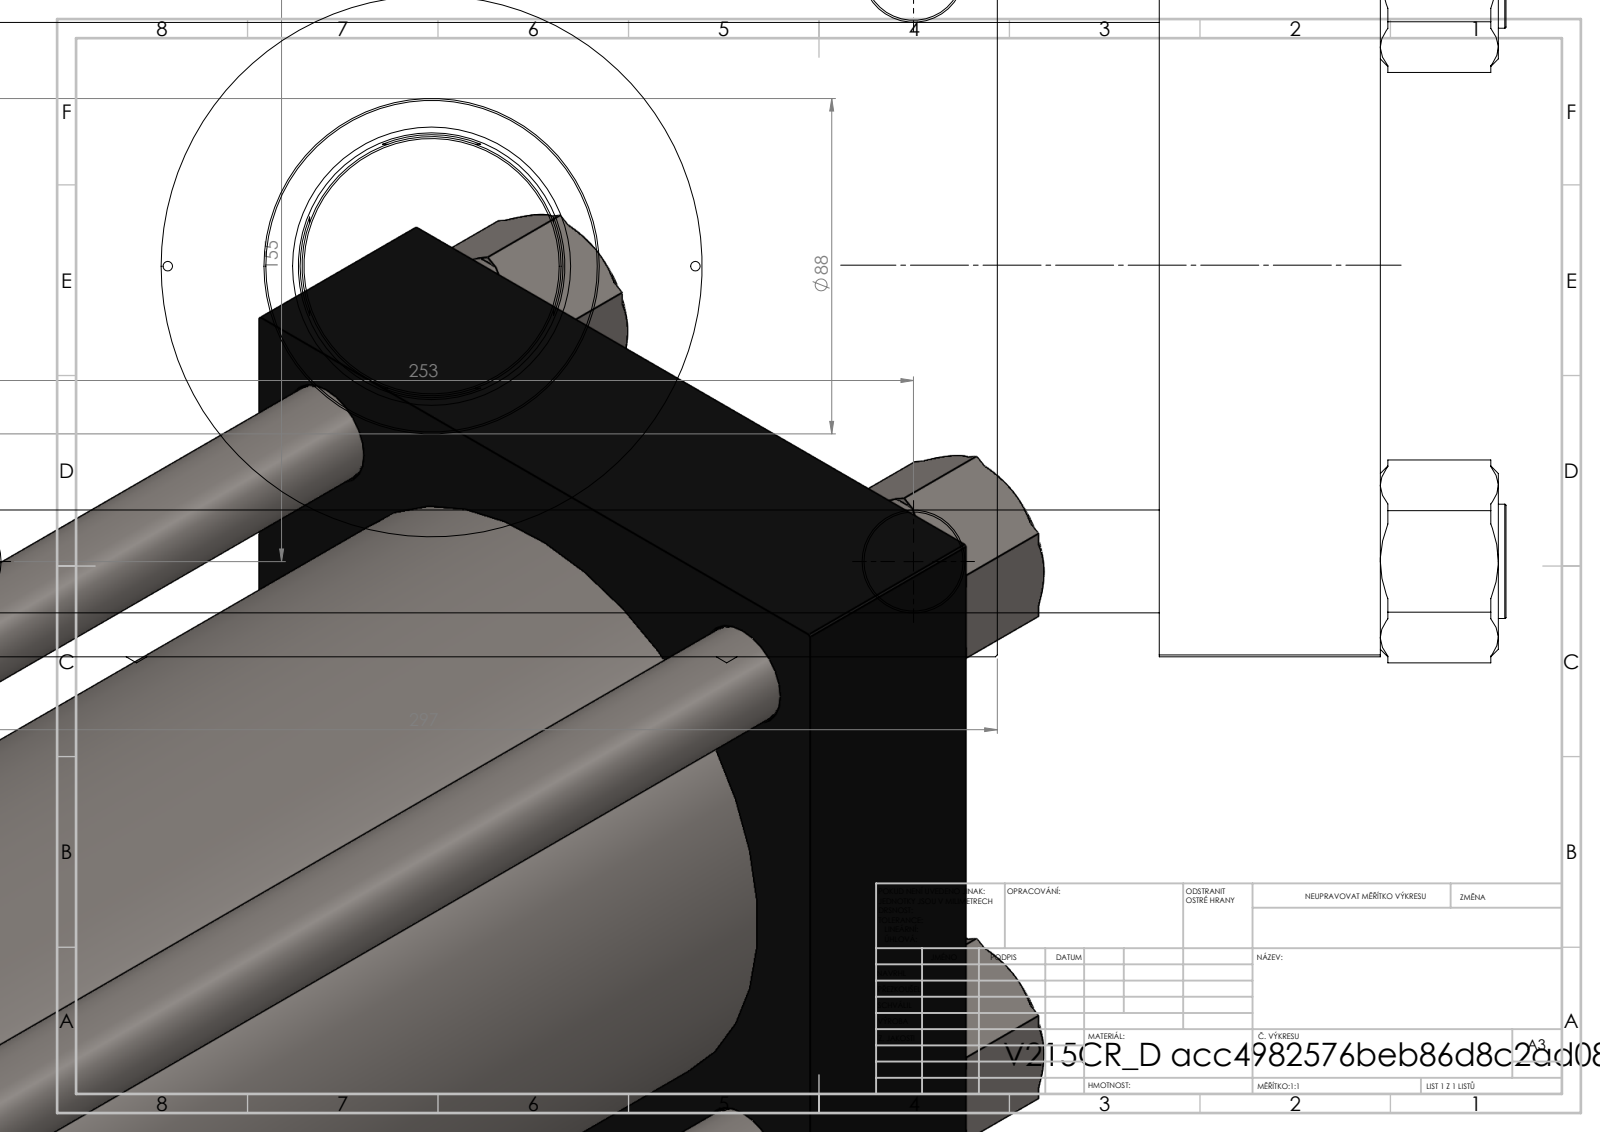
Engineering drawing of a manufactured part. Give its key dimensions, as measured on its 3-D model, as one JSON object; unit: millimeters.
{"part_name": "V215CR_D_TYCINKA; V215CR_VCP_D; V215_VC_A; V215CR_D_Body (+2 more)", "step_written_by": "SolidWorks 2019 (CONFIG_CONTROL_DESIGN)", "units": "millimeters", "bodies": {"solids": 12, "faces": 1168, "planar": 550, "cylindrical": 96, "other": 522}, "overall_size": [594, 297, 208.14], "volume_mm3": 9811000, "surface_area_mm2": 1114000, "round_holes": [[26, 4], [27, 4], [2.5, 2], [7, 2], [33.24, 2], [45, 2], [46.5, 1], [70, 1], [73, 1], [120, 1], [142, 1], [160, 1]], "round_bosses_or_shafts": [[30, 4], [166, 1], [88, 1], [68, 1], [50, 1], [49, 1]], "face_to_face_distances": [58, 380, 322, 436, 378, 56, 205, 46, 251, 72], "hole_center_spacings": [49.05, 77.88, 96.35, 109.53, 148.35, 154.9, 162.53, 165.89]}
